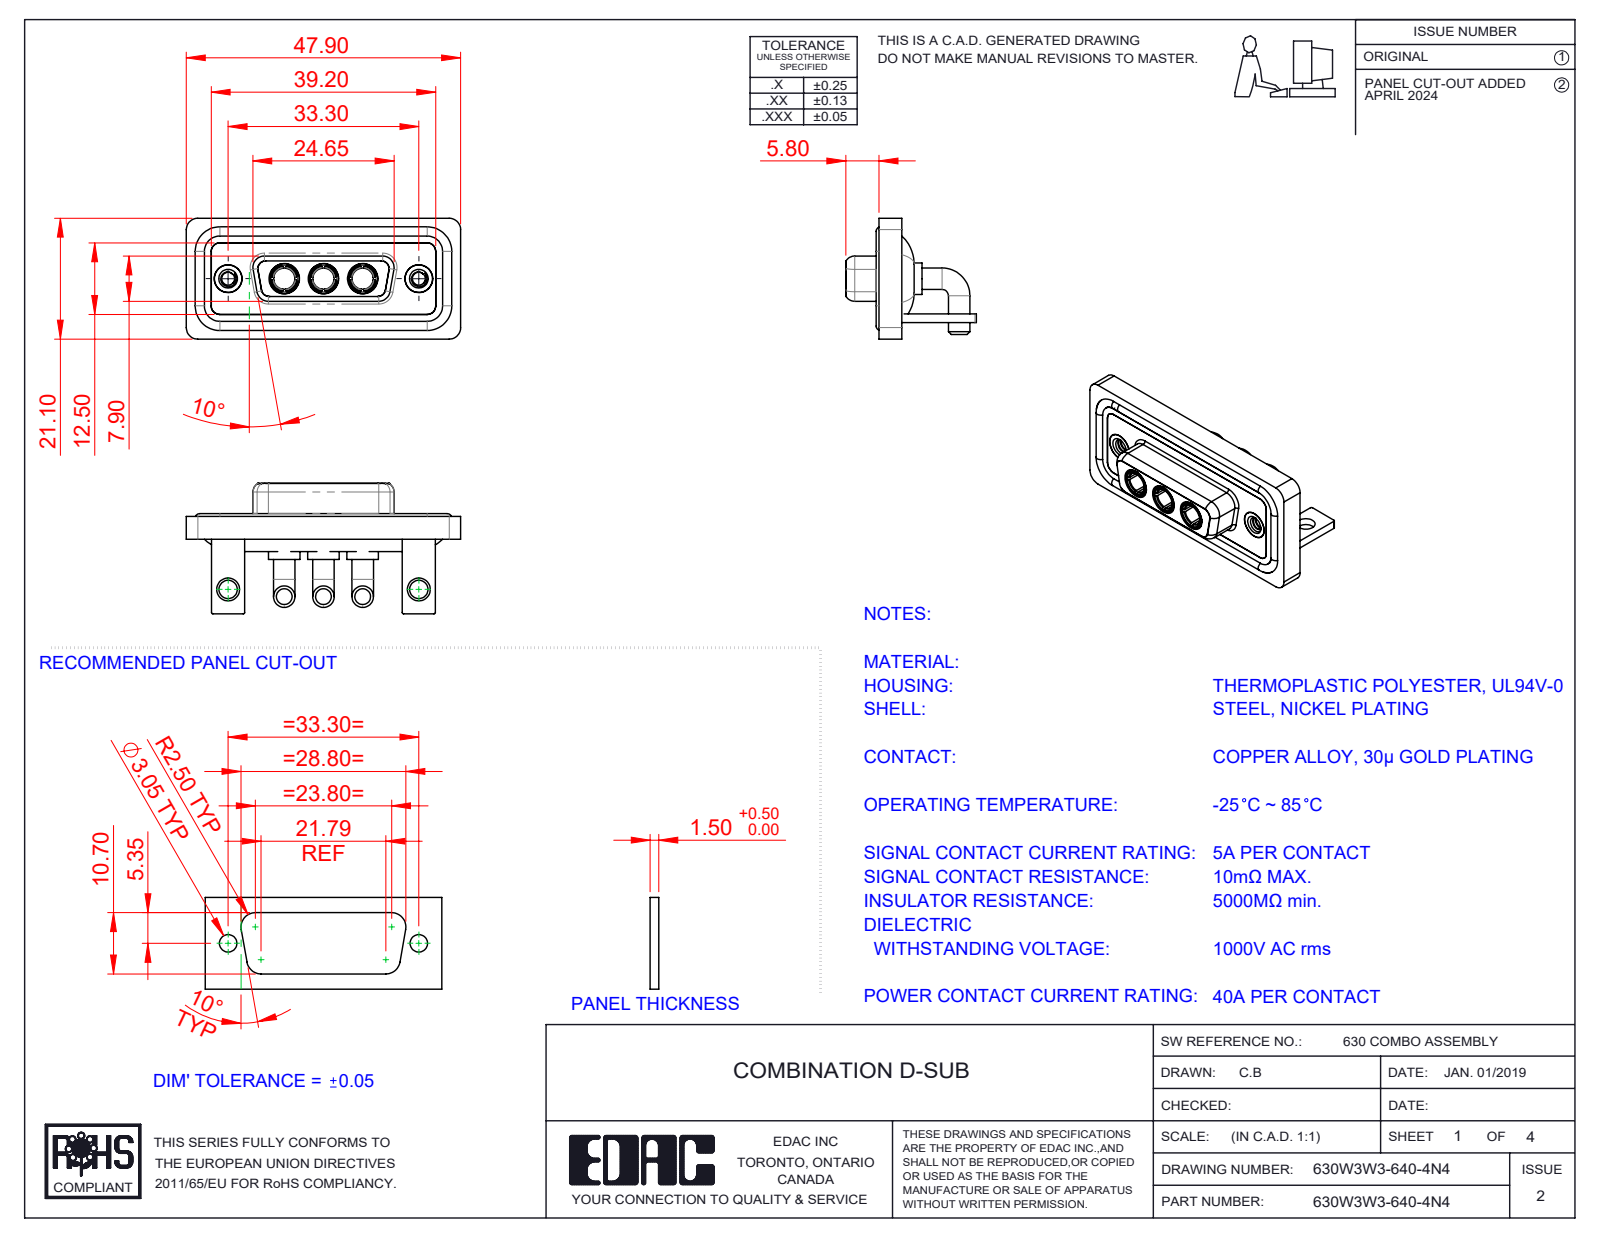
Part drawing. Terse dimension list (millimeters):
name: 630Combo Threaded Rivet_2; 630Combo Housing_3W3; 630Combo Stabilizer Bracket_50 Contacts; 630Combo Shell Front_15 Contacts (+4 more)
written by: SolidWorks 2023 (CONFIG_CONTROL_DESIGN)
unit: mm
bodies: 15 solids, 668 faces (212 planar, 287 cylindrical, 169 other)
size: 47.9 × 22.8 × 21.1
volume: 6 765 mm³; area: 10 838 mm²
holes: 5× ⌀4.85, 3× ⌀3.7, 3× ⌀5.3, 2× ⌀2.26, 2× ⌀3.2, 2× ⌀4, 2× ⌀4.05, 2× ⌀5
bosses: 6× ⌀3.75, 4× ⌀1.6, 3× ⌀5.5, 3× ⌀5.2, 3× ⌀4.96, 3× ⌀4.75, 2× ⌀4.95, 2× ⌀4.8
rounds: 21× R2, 18× R1.5, 16× R0.25, 12× R1.35, 8× R1.6, 5× R0.5, 4× R0.6, 4× R0.65
face distances: 0.4, 2.9, 1.5, 1.8, 3.7, 1.1, 4.1, 1.6, 2.5, 1.4
hole spacings: 6.85, 9.8, 16.65, 23.5, 33.3, 13.7
